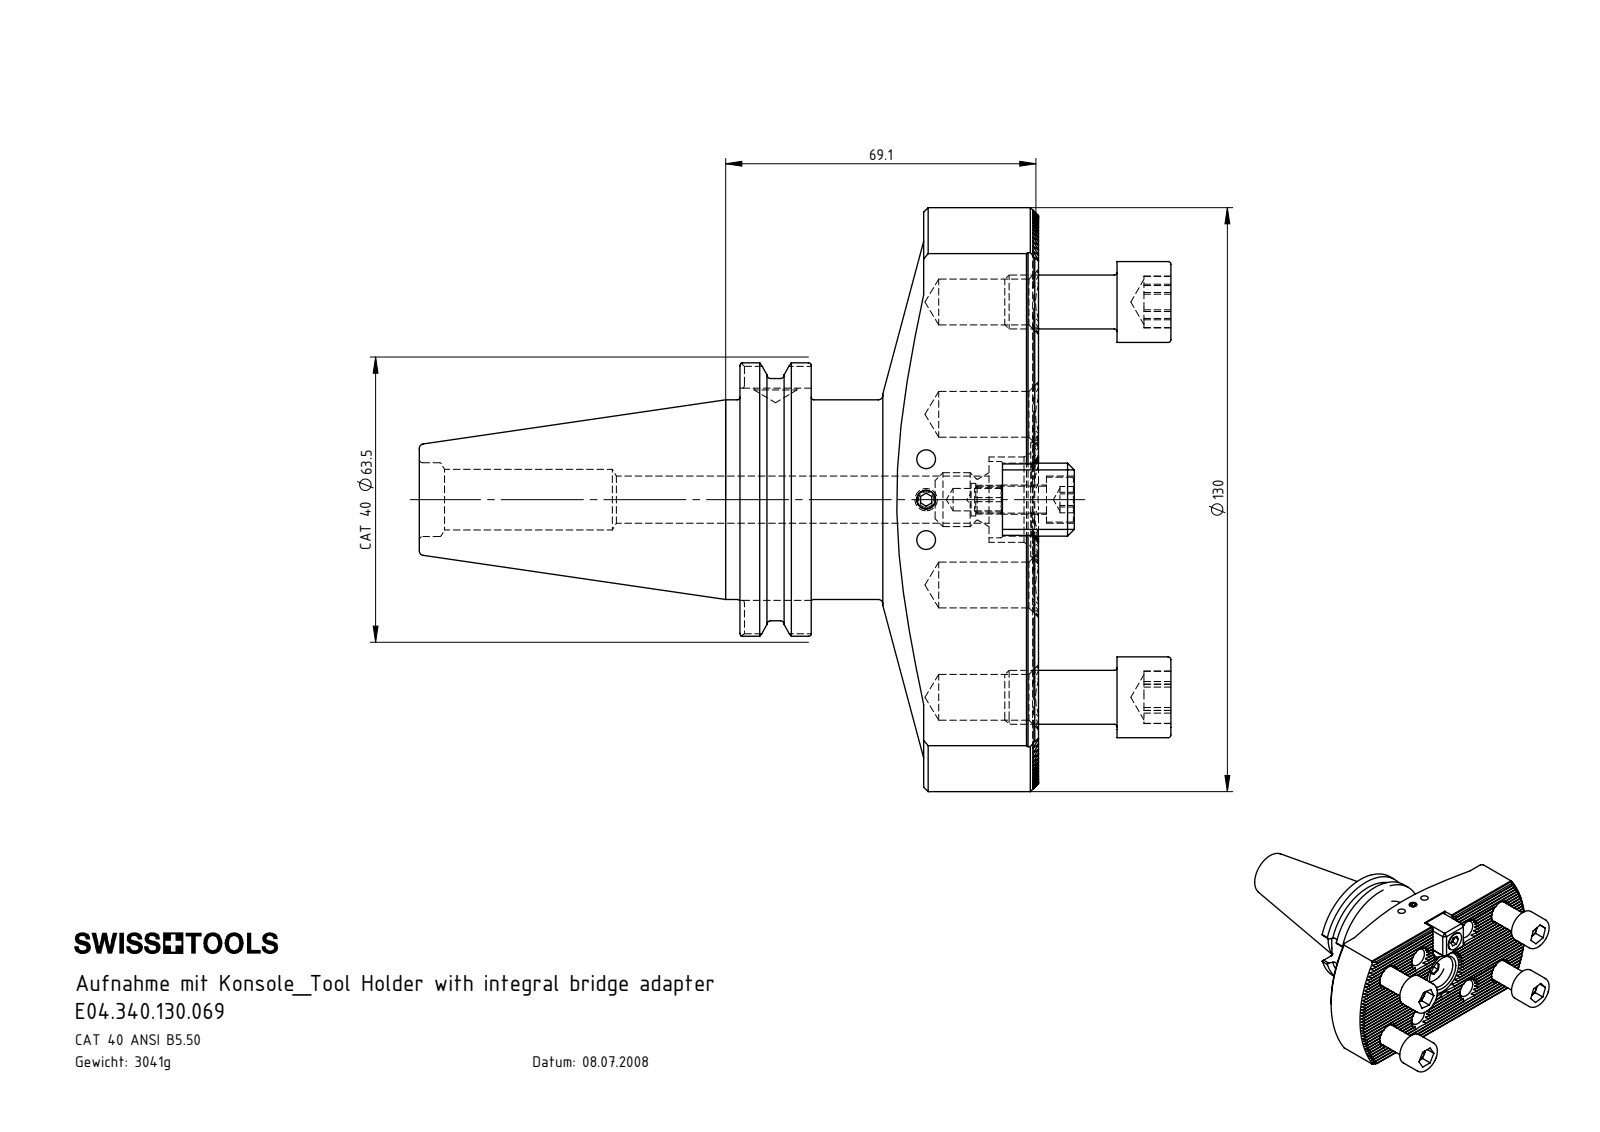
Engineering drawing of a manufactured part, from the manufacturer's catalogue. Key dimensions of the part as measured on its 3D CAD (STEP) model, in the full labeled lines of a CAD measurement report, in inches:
Part name (STEP PRODUCT): E04.340.130.069; Ko1-ER1.001.016_A; ISO 4762 M6 x 16; ISO 4762 M12 x 25 (+3 more)
STEP written by: SolidWorks 2017 (CONFIG_CONTROL_DESIGN)
Units: inches
Bodies: 10 solids, 856 faces (496 planar, 201 cylindrical, 159 other)
Overall size (bounding box): 6.591 × 5.118 × 2.756
Volume: 23.64 in³ · Surface area: 112.9 in²
Round holes (diameter × count): ⌀0.402 ×8, ⌀0.165 ×3, ⌀0.413 ×2, ⌀0.197 ×1, ⌀0.256 ×1, ⌀0.285 ×1, ⌀0.374 ×1, ⌀0.531 ×1, ⌀0.647 ×1, ⌀0.748 ×1
Round bosses / shafts (diameter × count): ⌀0.472 ×5, ⌀0.709 ×4, ⌀2.5 ×1, ⌀2.219 ×1, ⌀1.75 ×1, ⌀0.669 ×1, ⌀0.394 ×1, ⌀0.236 ×1
Partial cylindrical surfaces — rounded edges, fillets, slot ends (radius × count): R0.006 ×34, R0.031 ×8, R0.313 ×1, R2.559 ×1
Main face-to-face distances: 0.068, 0.682, 2.756, 0.341, 0.136, 0.205, 0.273, 0.614, 0.75, 0.137
Hole centre spacings: 0.984, 1.086, 1.575, 1.857, 1.903, 2.48, 2.938, 0.354
